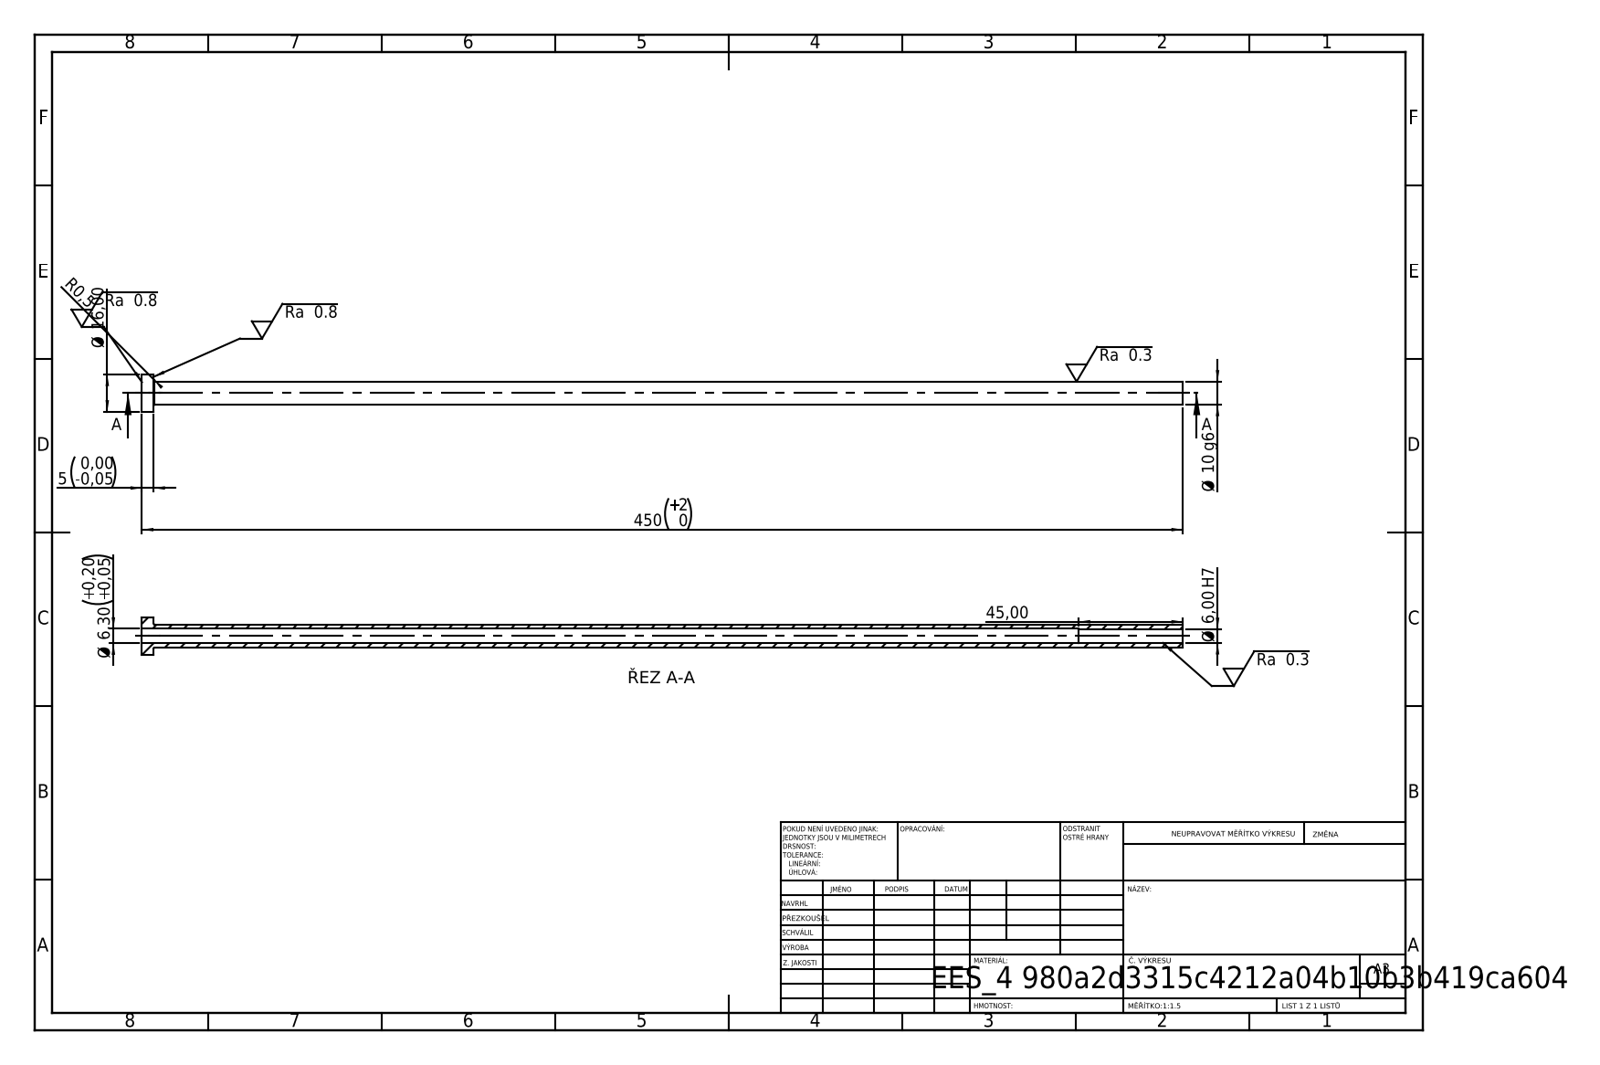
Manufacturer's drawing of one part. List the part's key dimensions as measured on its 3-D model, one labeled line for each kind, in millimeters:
STEP written by: SolidWorks 2019 (CONFIG_CONTROL_DESIGN)
Units: millimetres
Bodies: 1 solid, 14 faces (4 planar, 8 cylindrical, 2 other)
Overall size (bounding box): 450 × 16 × 16
Volume: 22 060 mm³ · Surface area: 23 434 mm²
Round holes (diameter × count): ⌀6 ×1, ⌀6.3 ×1
Round bosses / shafts (diameter × count): ⌀16 ×1, ⌀10 ×1
Main face-to-face distances: 5, 450, 445, 405, 400, 45
